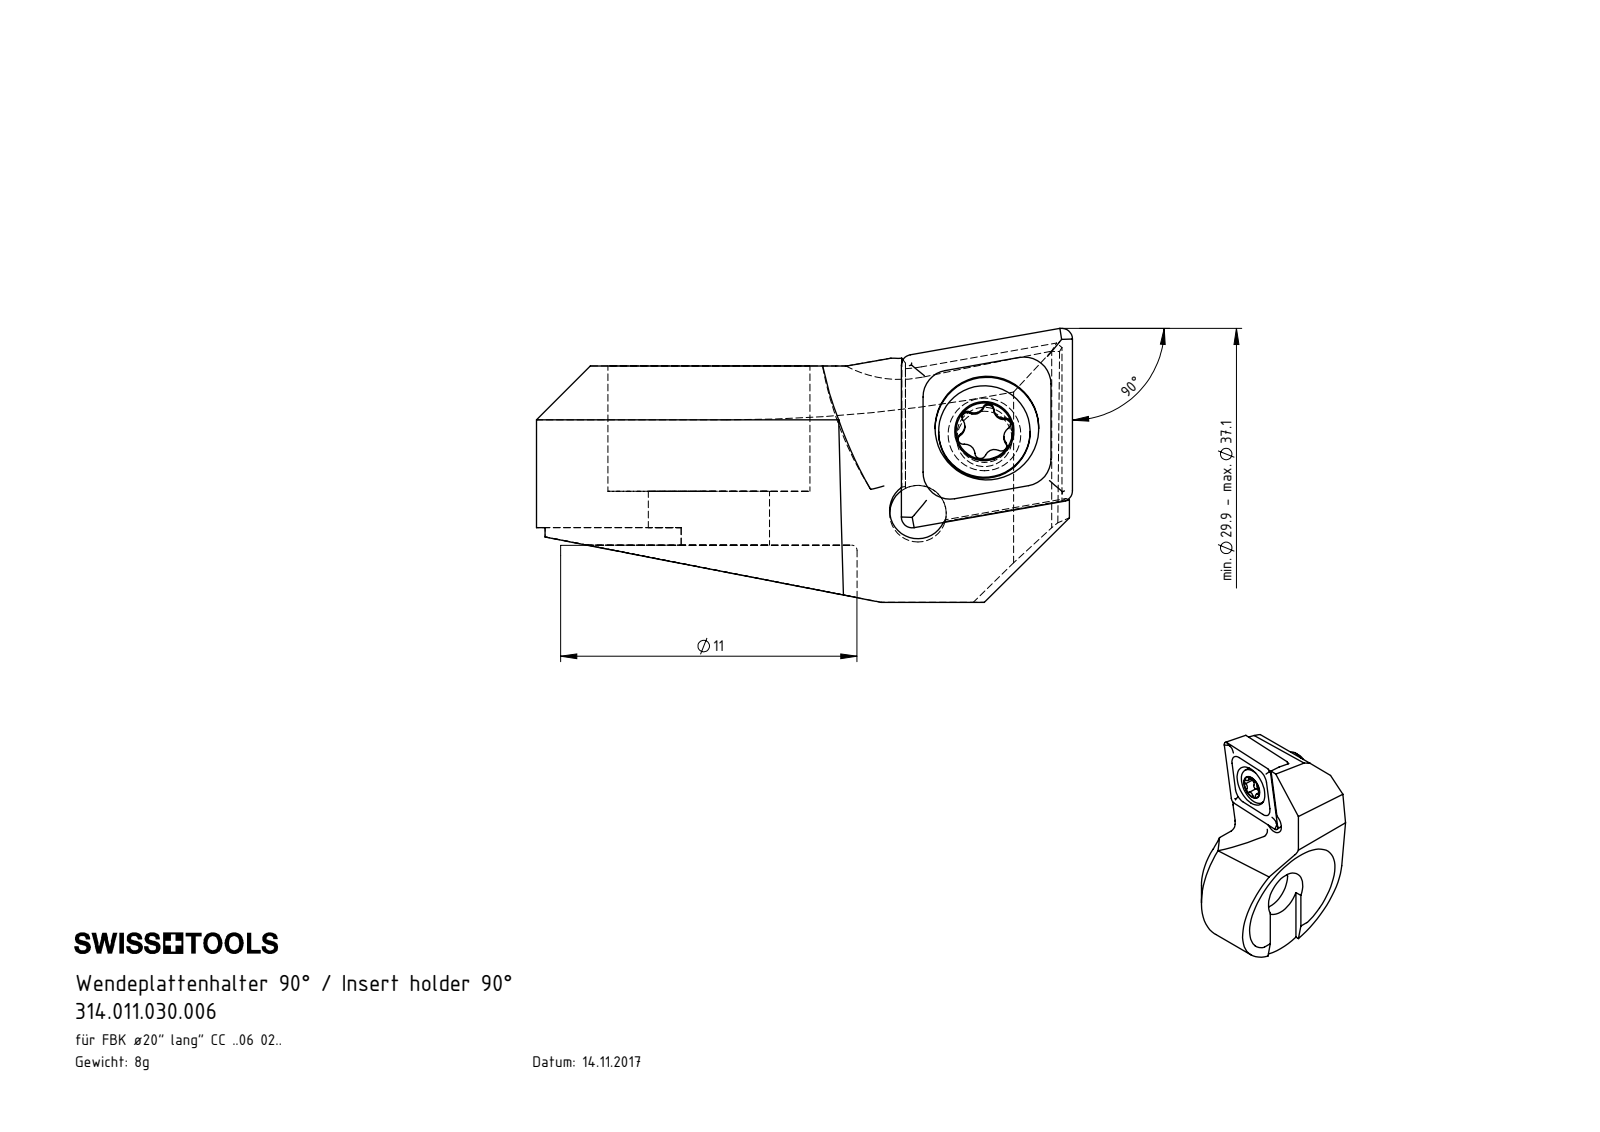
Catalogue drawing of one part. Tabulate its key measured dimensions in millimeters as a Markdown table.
| quantity | value |
| --- | --- |
| part name | 314.011.030.006; CCMT060204; F20-WCA.001.008_C_fertigbearbeitet; WCA-ER2.001.006_A |
| STEP written by | SolidWorks 2017 (CONFIG_CONTROL_DESIGN) |
| units | millimeters |
| bodies | 5 solids, 146 faces (49 planar, 46 cylindrical, 51 other) |
| overall size | 19.9 × 12.8 × 10.17 |
| volume | 1 042 mm³ |
| surface area | 1 316 mm² |
| round holes (diameter × count) | 2.05 × 1, 2.1 × 1, 2.8 × 1, 3.85 × 1, 4.5 × 1, 7.5 × 1 |
| round bosses / shafts (diameter × count) | 3.4 × 1, 2.5 × 1 |
| partial cylindrical surfaces (radius × count) | 0.21 × 6, 0.36 × 5, 0.5 × 2, 0.36 × 1, 1.05 × 1, 5 × 1, 5.5 × 1, 6.4 × 1 |
| main face-to-face distances | 2.28, 6.65, 1, 5.65, 4.65, 3.65, 2, 8.77, 7.77, 4.12 |
| hole center spacings | 3.84, 4 |
